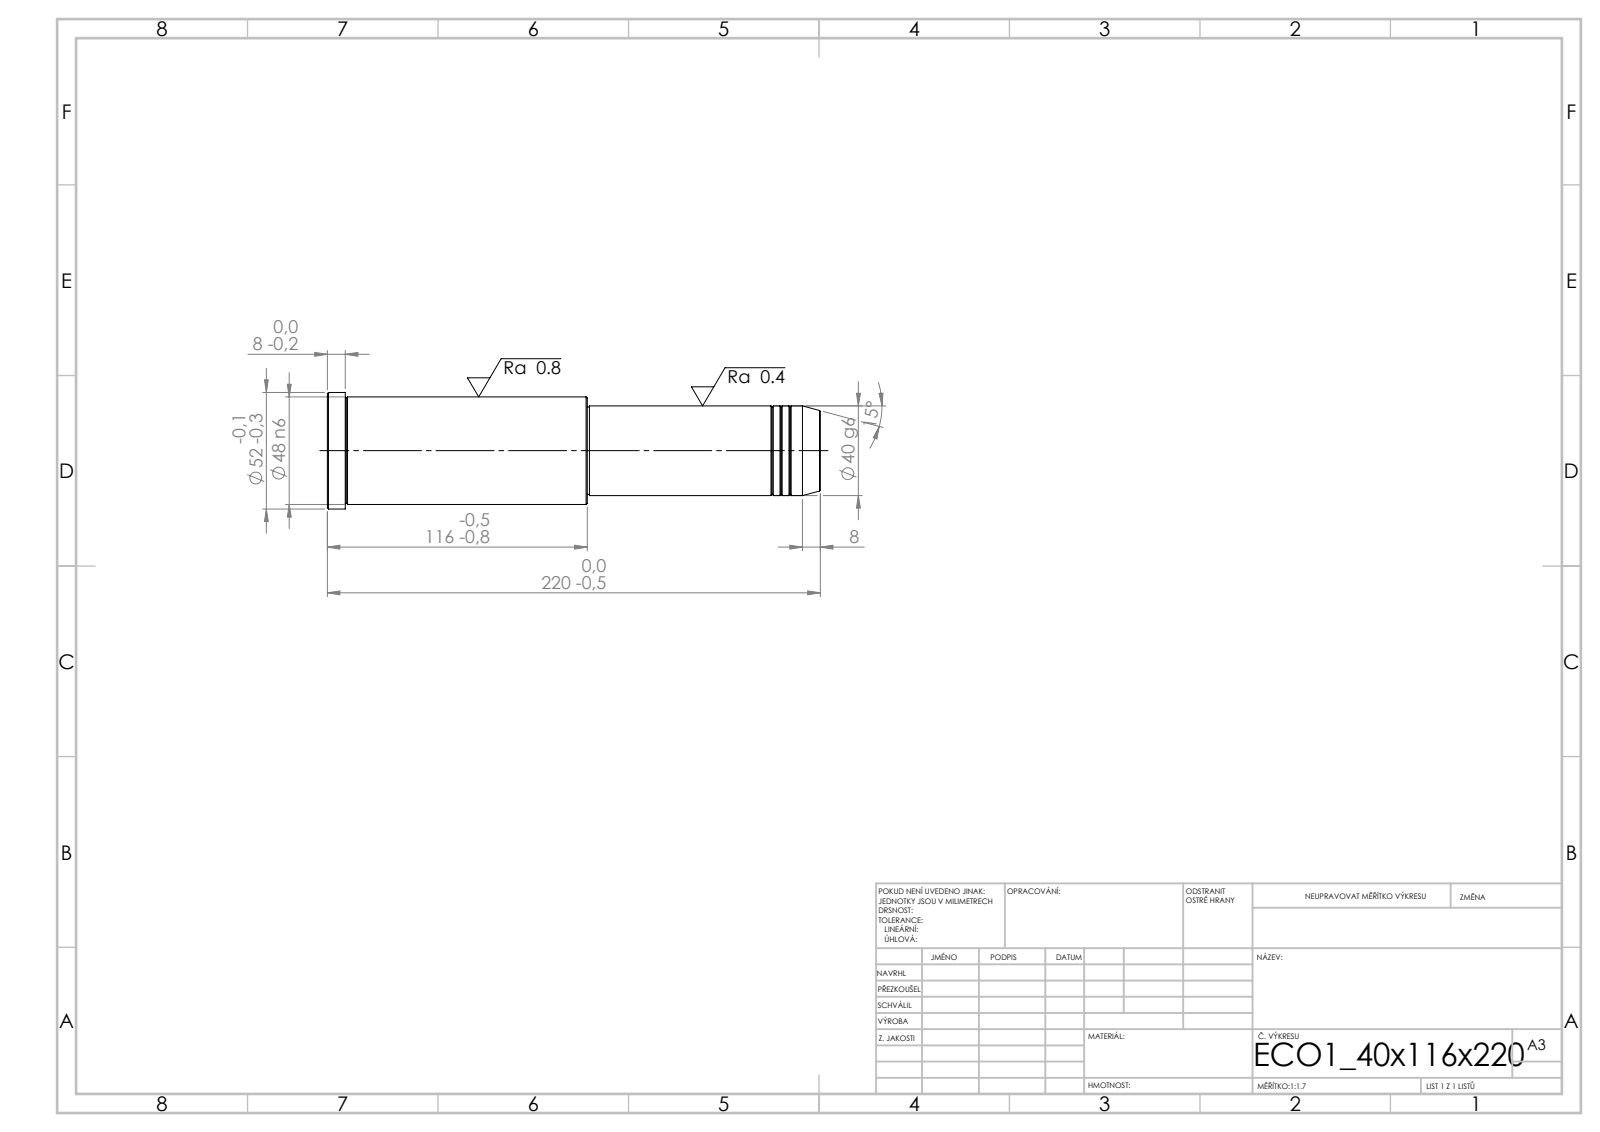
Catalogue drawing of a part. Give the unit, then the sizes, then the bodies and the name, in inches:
Units: inches
Overall size (bounding box): 8.661 × 2.047 × 2.047
Round bosses / shafts (diameter × count): ⌀2.047 ×1, ⌀1.89 ×1, ⌀1.575 ×1, ⌀1.535 ×1
Main face-to-face distances: 8.661, 4.094, 4.567, 8.346, 4.252, 0.315, 4.055, 0.039, 4.291, 4.606
Volume: 20.86 in³ · Surface area: 54.15 in²
Bodies: 1 solid, 43 faces (5 planar, 14 cylindrical, 24 other)
STEP written by: SolidWorks 2019 (CONFIG_CONTROL_DESIGN)
